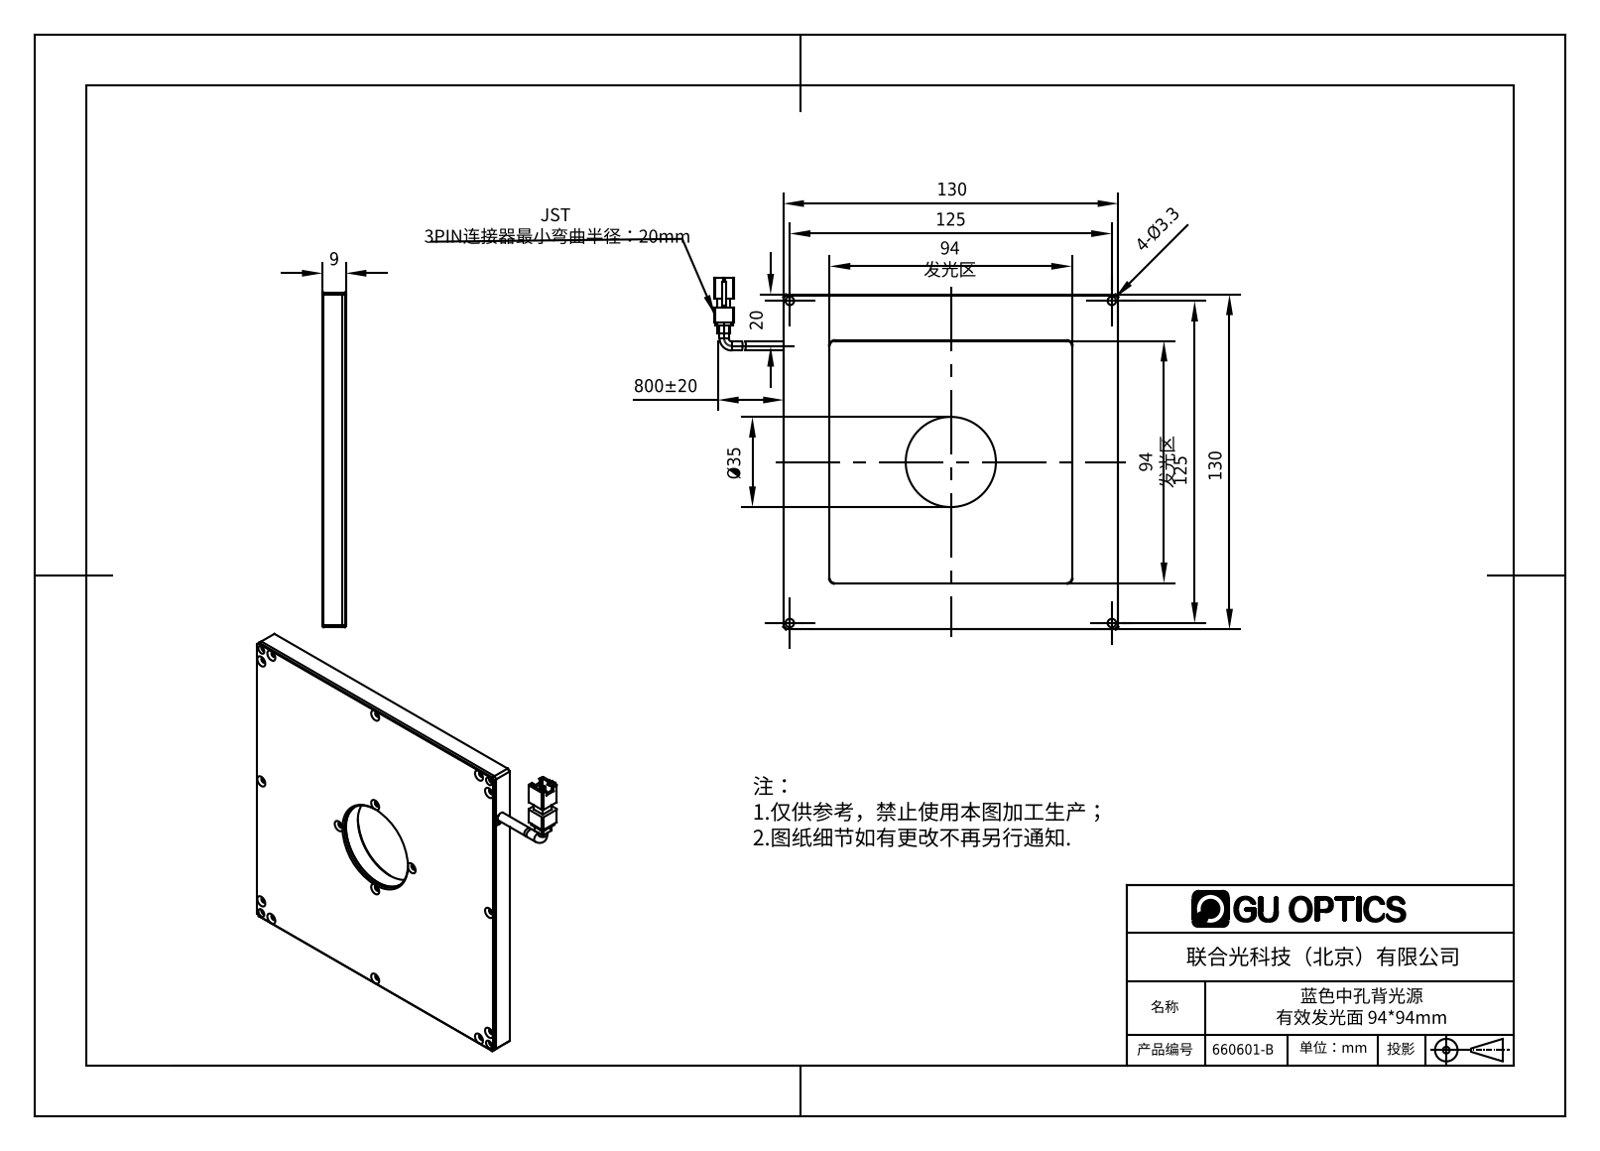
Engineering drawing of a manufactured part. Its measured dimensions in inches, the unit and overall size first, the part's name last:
Units: inches
Overall size (bounding box): 6.181 × 5.374 × 0.394
Round holes (diameter × count): ⌀0.063 ×16, ⌀0.079 ×12, ⌀0.087 ×12, ⌀0.094 ×4, ⌀0.13 ×4, ⌀1.378 ×1, ⌀1.693 ×1
Round bosses / shafts (diameter × count): ⌀0.138 ×2, ⌀1.803 ×1, ⌀1.685 ×1
Partial cylindrical surfaces — rounded edges, fillets, slot ends (radius × count): R0.02 ×8, R0.059 ×6, R0.039 ×4, R0.079 ×4, R0.063 ×1
Main face-to-face distances: 0.157, 0.256, 0.059, 0.315, 0.098, 0.354, 0.197, 0.039, 0.295, 4.961
Hole centre spacings: 2.461, 4.921, 0.217, 2.244, 2.47, 2.583, 2.799, 2.859
Volume: 5.691 in³ · Surface area: 133 in²
Bodies: 6 solids, 474 faces (191 planar, 148 cylindrical, 135 other)
Part name (STEP PRODUCT): 660601-B
STEP written by: SolidWorks 2016 (AUTOMOTIVE_DESIGN)
